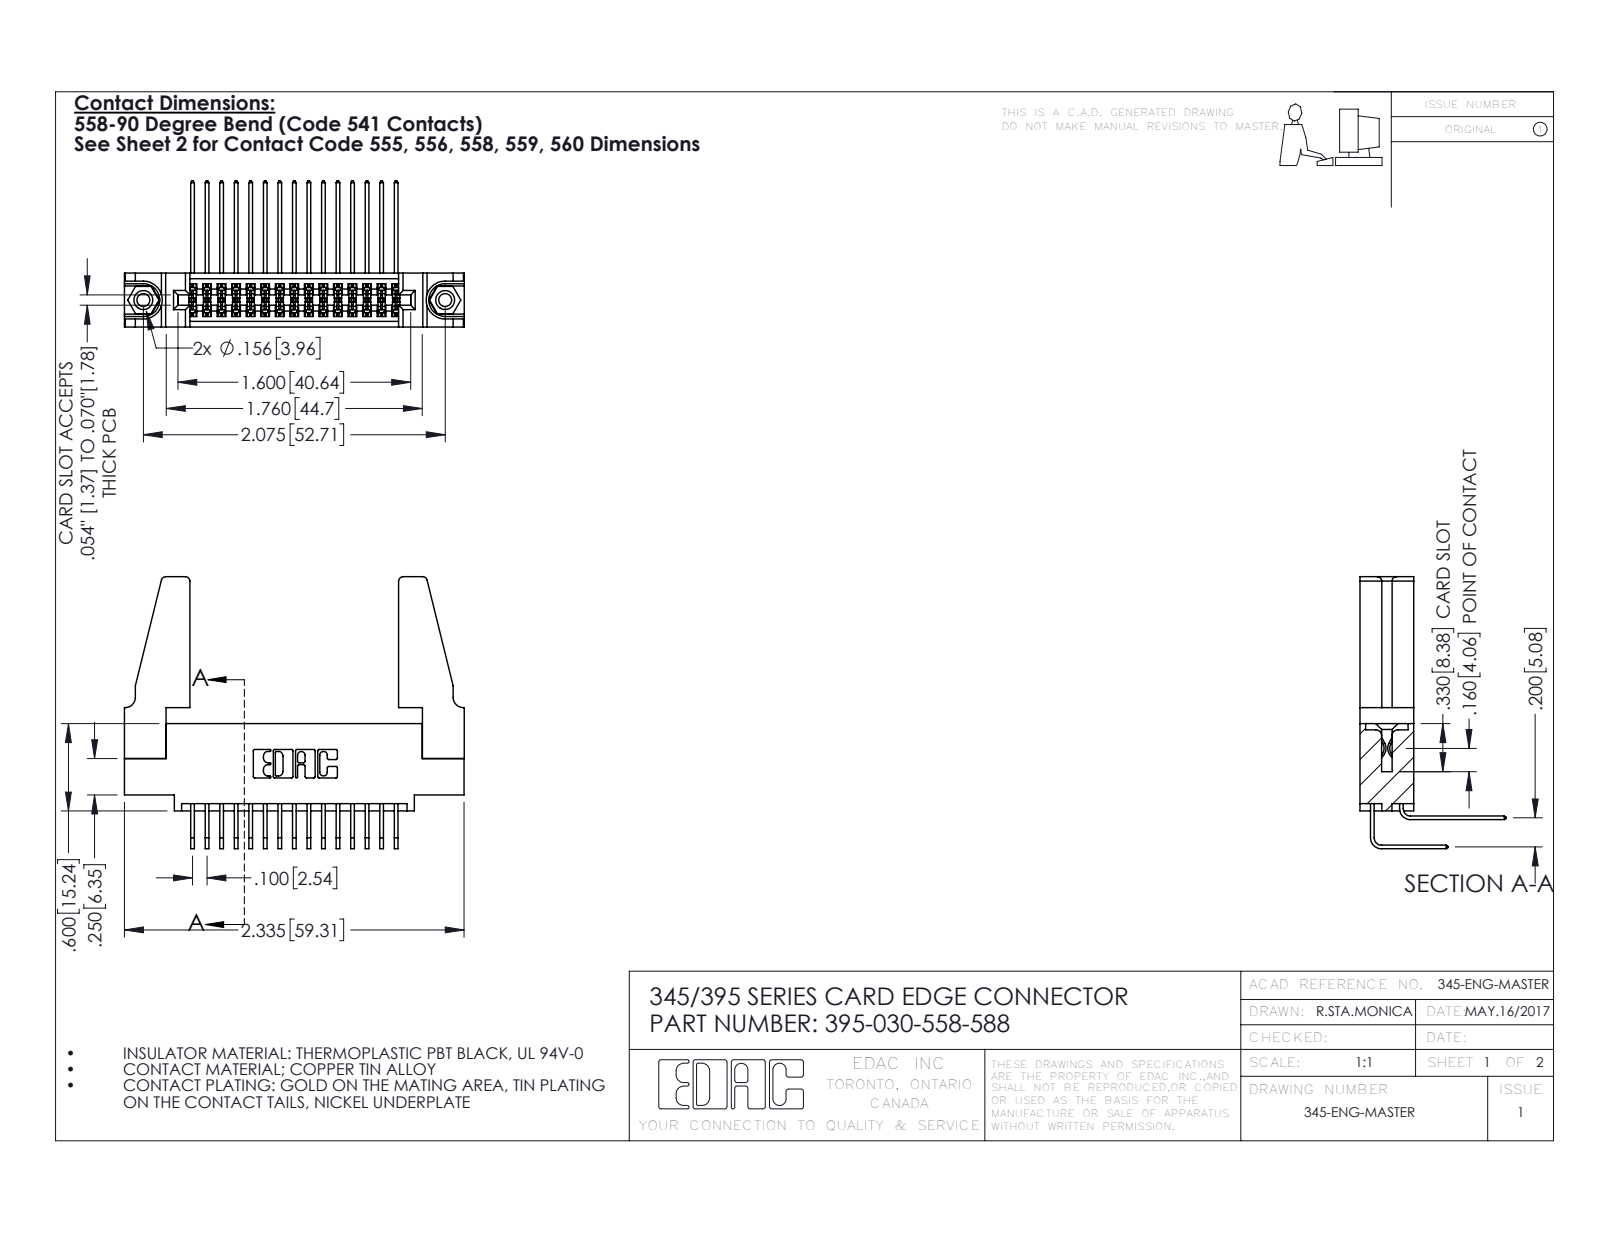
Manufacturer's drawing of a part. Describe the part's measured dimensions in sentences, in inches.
The part is named "345 Part_0.110 Offset - 0.156 Dia-TH; 345-292-001_558 559 Tail - 1; 395-030-558-588; 345-220-078_345-220-088 (+2 more)". Its 3-D file was written by "SolidWorks 2016 (CONFIG_CONTROL_DESIGN)". It is 35 solids with 1814 faces: 1206 planar, 592 cylindrical and 16 other. Overall it measures 2.336 by 1.869 by 1.005 inches. Its volume is 0.541 cubic inches and its surface area 18.29 square inches. Round holes: 2 of diameter 0.089, 2 of diameter 0.125, 2 of diameter 0.156, 1 of diameter 0.064. Round bosses or shafts: 2 of diameter 0.155. Partial cylindrical surfaces (rounded edges, fillets, slot ends): 46 of radius 0.006, 22 of radius 0.01, 8 of radius 0.03, 6 of radius 0.007, 6 of radius 0.031, 3 of radius 0.026, 2 of radius 0.014, 2 of radius 0.019. The main face-to-face distances are 0.37, 0.072, 0.298, 0.2, 0.098, 0.272, 0.025, 0.225, 0.148, 0.15. The hole center spacings are 0.27, 1.842, 2.075.
